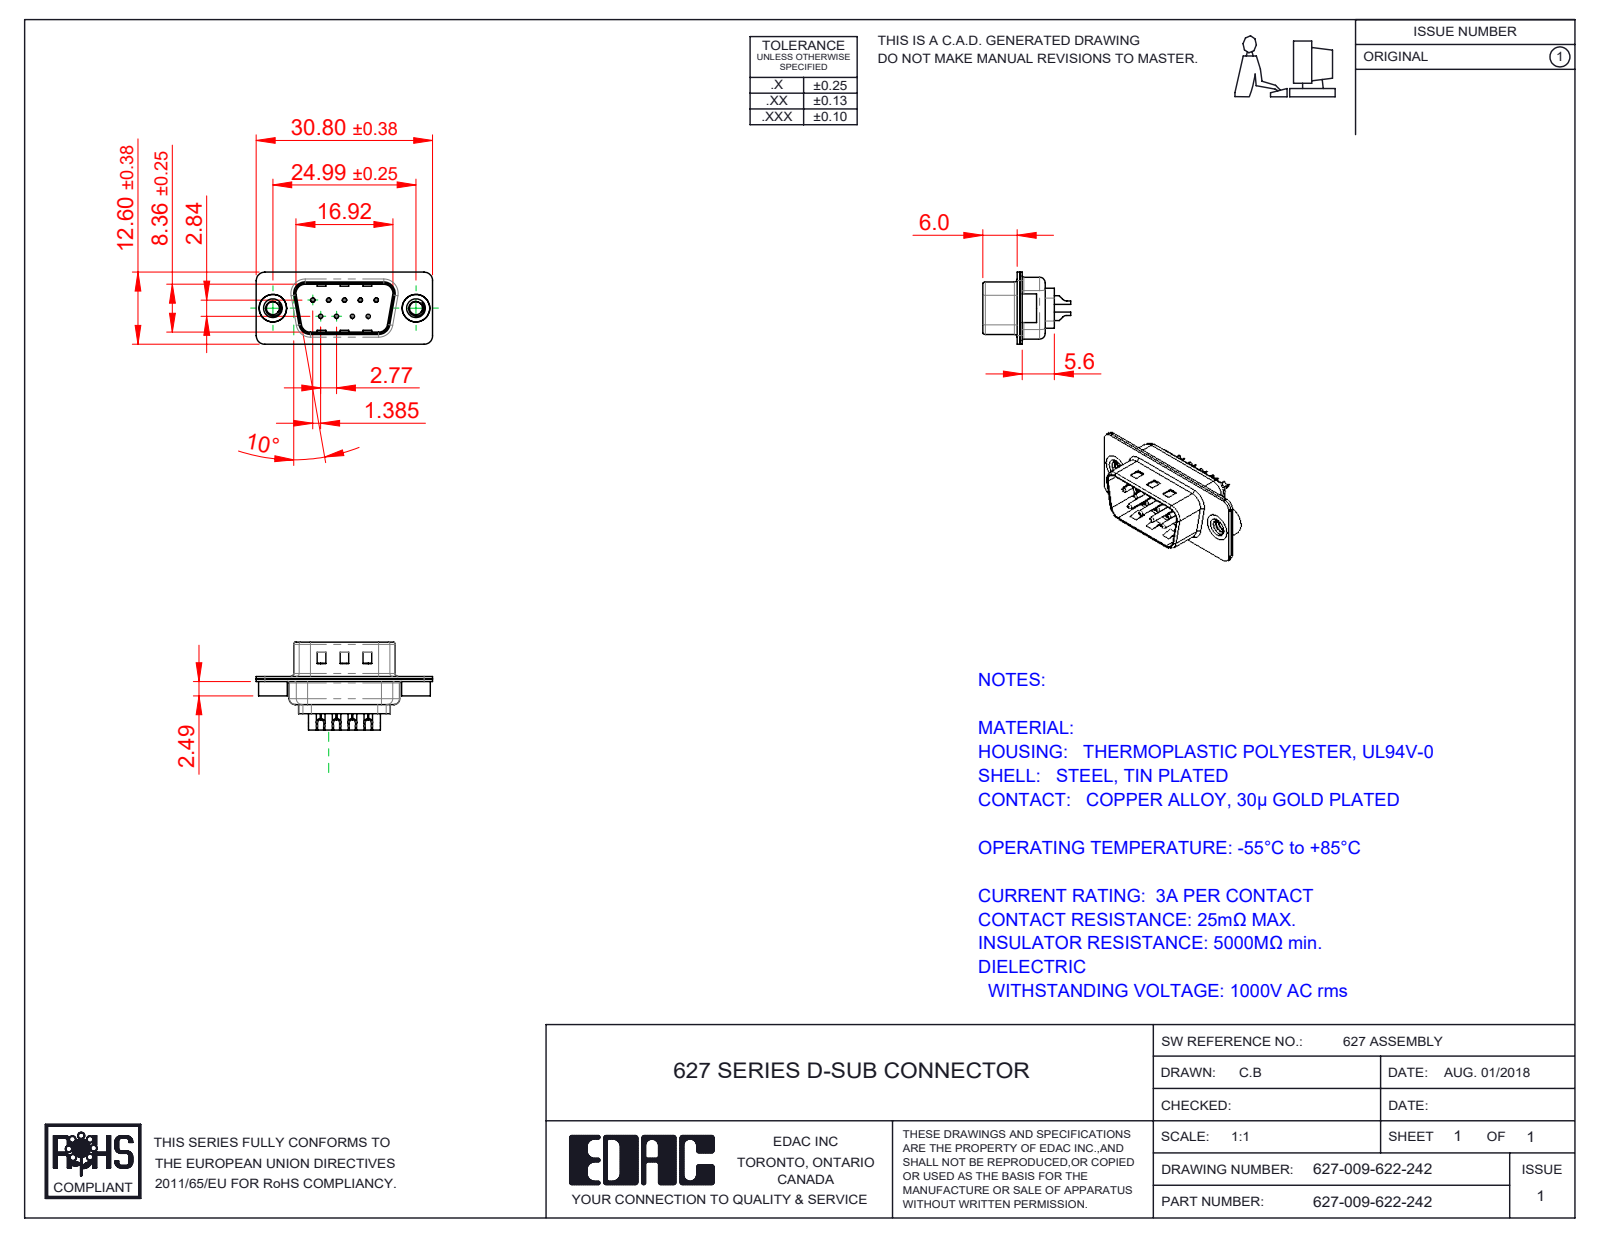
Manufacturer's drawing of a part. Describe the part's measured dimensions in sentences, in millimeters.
The part is named "627 Shell Rear_09 Contacts; 627 Contact Row 1_22L; 627 Shell Front_09 Contacts; 627 4-40 Threaded Rivet (+3 more)". Its 3-D file was written by "SolidWorks 2020 (CONFIG_CONTROL_DESIGN)". It is 14 solids with 876 faces: 233 planar, 388 cylindrical and 255 other. Overall it measures 30.8 by 15.35 by 12.6 millimeters. Its volume is 1 311 cubic millimeters and its surface area 3 942 square millimeters. Round holes: 9 of diameter 0.35, 9 of diameter 1.1, 9 of diameter 1.6, 2 of diameter 2.26, 2 of diameter 4, 2 of diameter 4.8. Round bosses or shafts: 9 of diameter 2, 9 of diameter 1.5, 9 of diameter 0.75, 2 of diameter 5, 2 of diameter 4.9. Partial cylindrical surfaces (rounded edges, fillets, slot ends): 18 of radius 1.5, 12 of radius 2, 8 of radius 0.5, 8 of radius 1.6, 6 of radius 1, 4 of radius 0.25, 4 of radius 0.6, 4 of radius 0.65. The main face-to-face distances are 0.45, 0.4, 0.9, 0.82, 9.58, 1.4, 8.76, 0.5, 1.5, 6.5. The hole center spacings are 3.16, 2.77, 5.54, 5.03, 5.04, 8.31, 7.48, 7.49.
